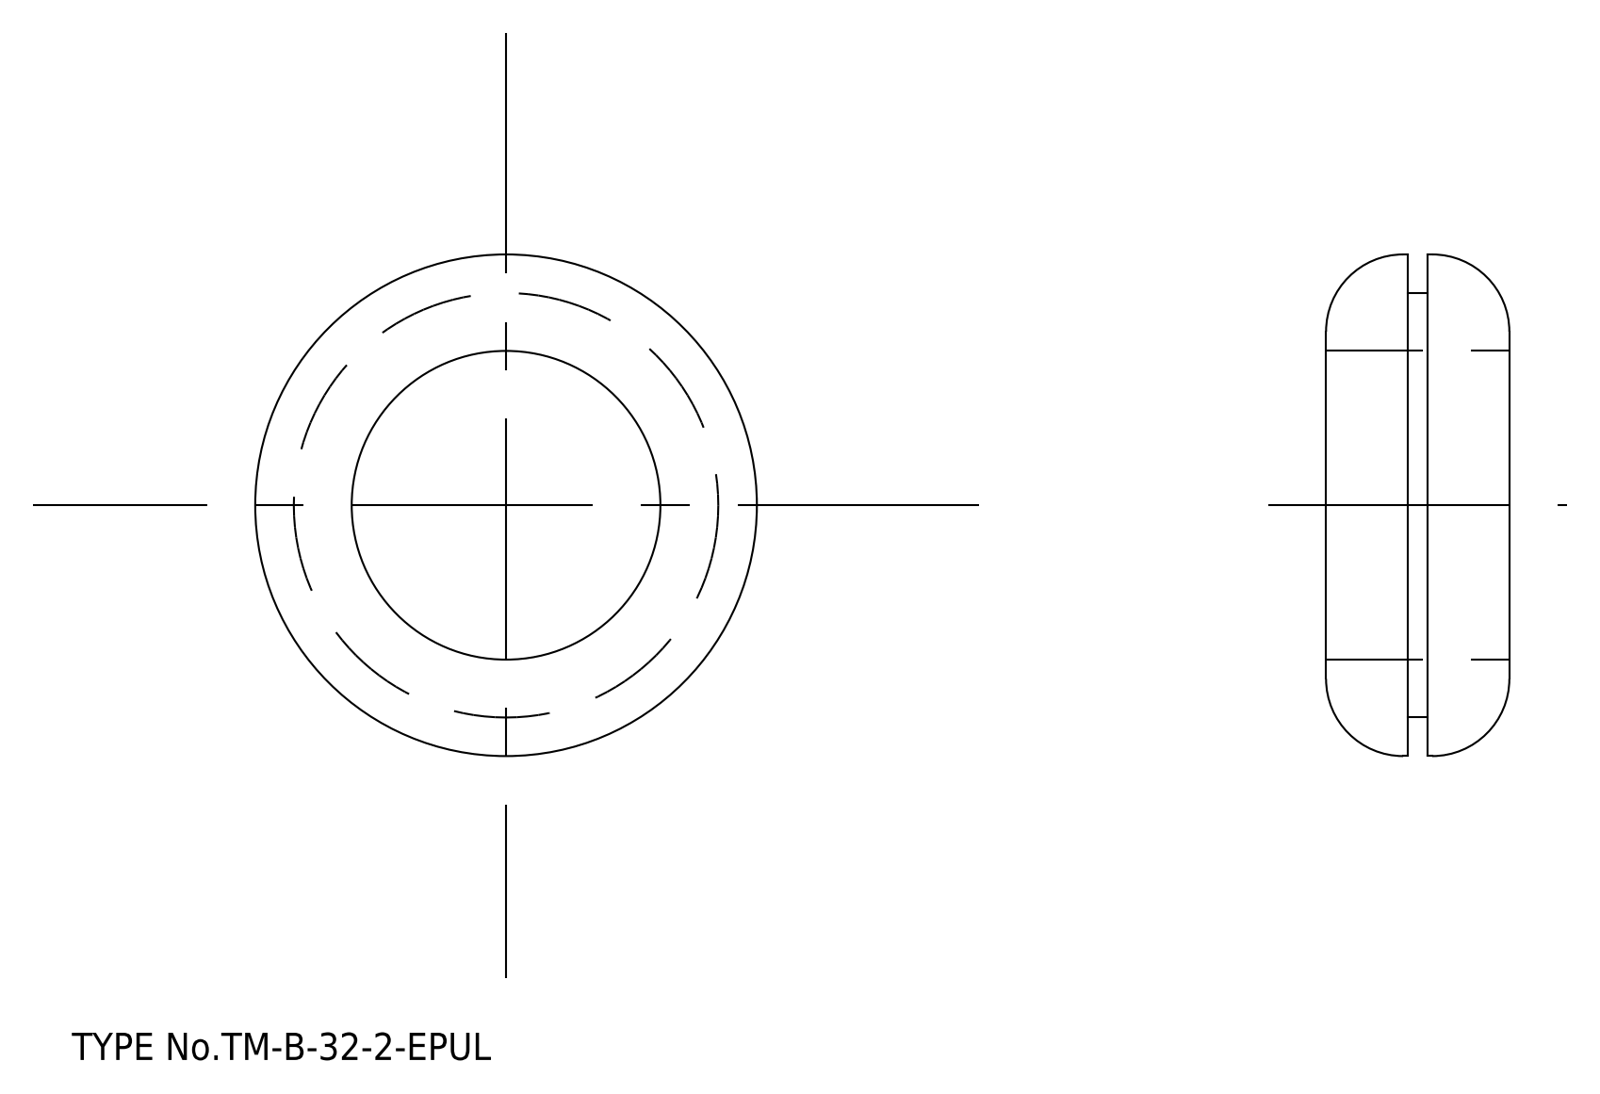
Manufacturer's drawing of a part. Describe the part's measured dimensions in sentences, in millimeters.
Its 3-D file was written by "spGate 15.6.1 (AUTOMOTIVE_DESIGN)". It is 1 solid with 16 faces: 4 planar, 8 cylindrical and 4 other. Overall it measures 52 by 52 by 19 millimeters. Its volume is 19 684 cubic millimeters and its surface area 7 628 square millimeters. Round holes: 1 of diameter 32. Round bosses or shafts: 1 of diameter 52, 1 of diameter 44. The main face-to-face distances are 2, 8.5, 10.5, 19.
